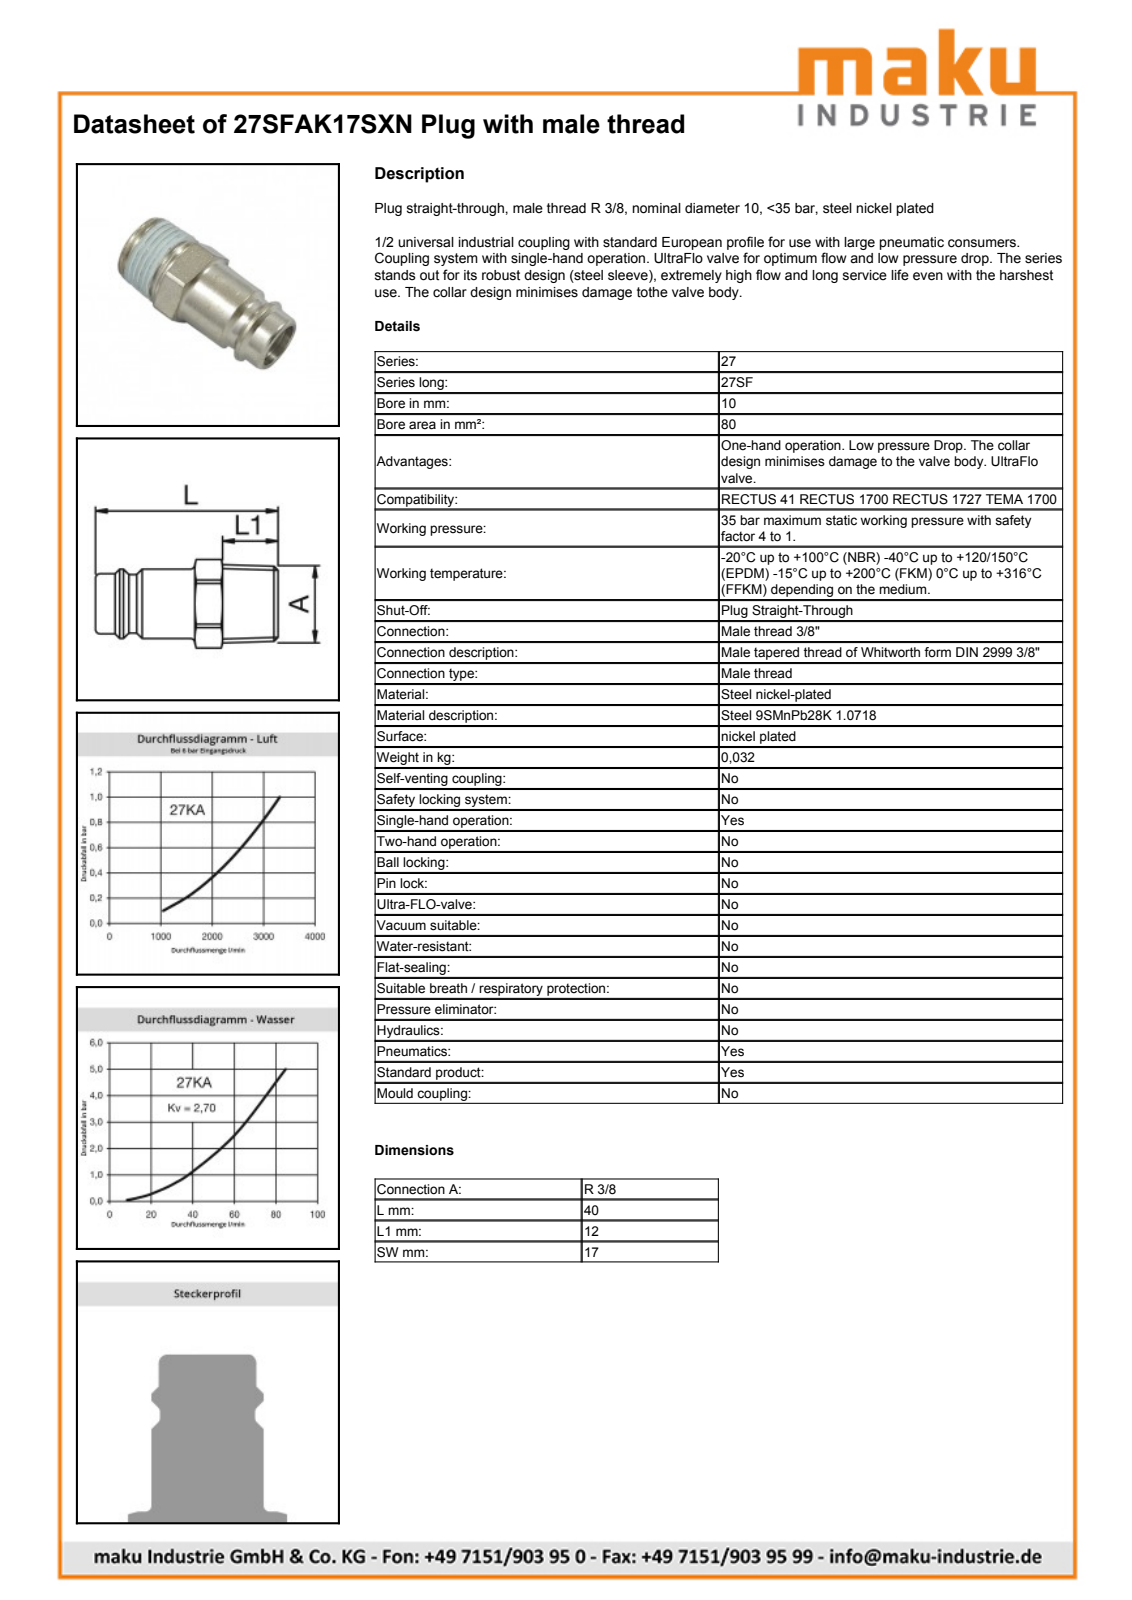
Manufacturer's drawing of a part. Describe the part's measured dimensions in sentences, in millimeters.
The part is named "D106712". Its 3-D file was written by "Autodesk Inventor 2011 (AUTOMOTIVE_DESIGN)". It is 1 solid with 41 faces: 8 planar, 11 cylindrical and 22 other. Overall it measures 39.5 by 19.15 by 17 millimeters. Its volume is 4 409 cubic millimeters and its surface area 3 422 square millimeters. Round holes: 1 of diameter 10. Round bosses or shafts: 1 of diameter 15, 1 of diameter 13, 1 of diameter 12.65. Partial cylindrical surfaces (rounded edges, fillets, slot ends): 1 of radius 9.57. The main face-to-face distances are 17, 39.5.
